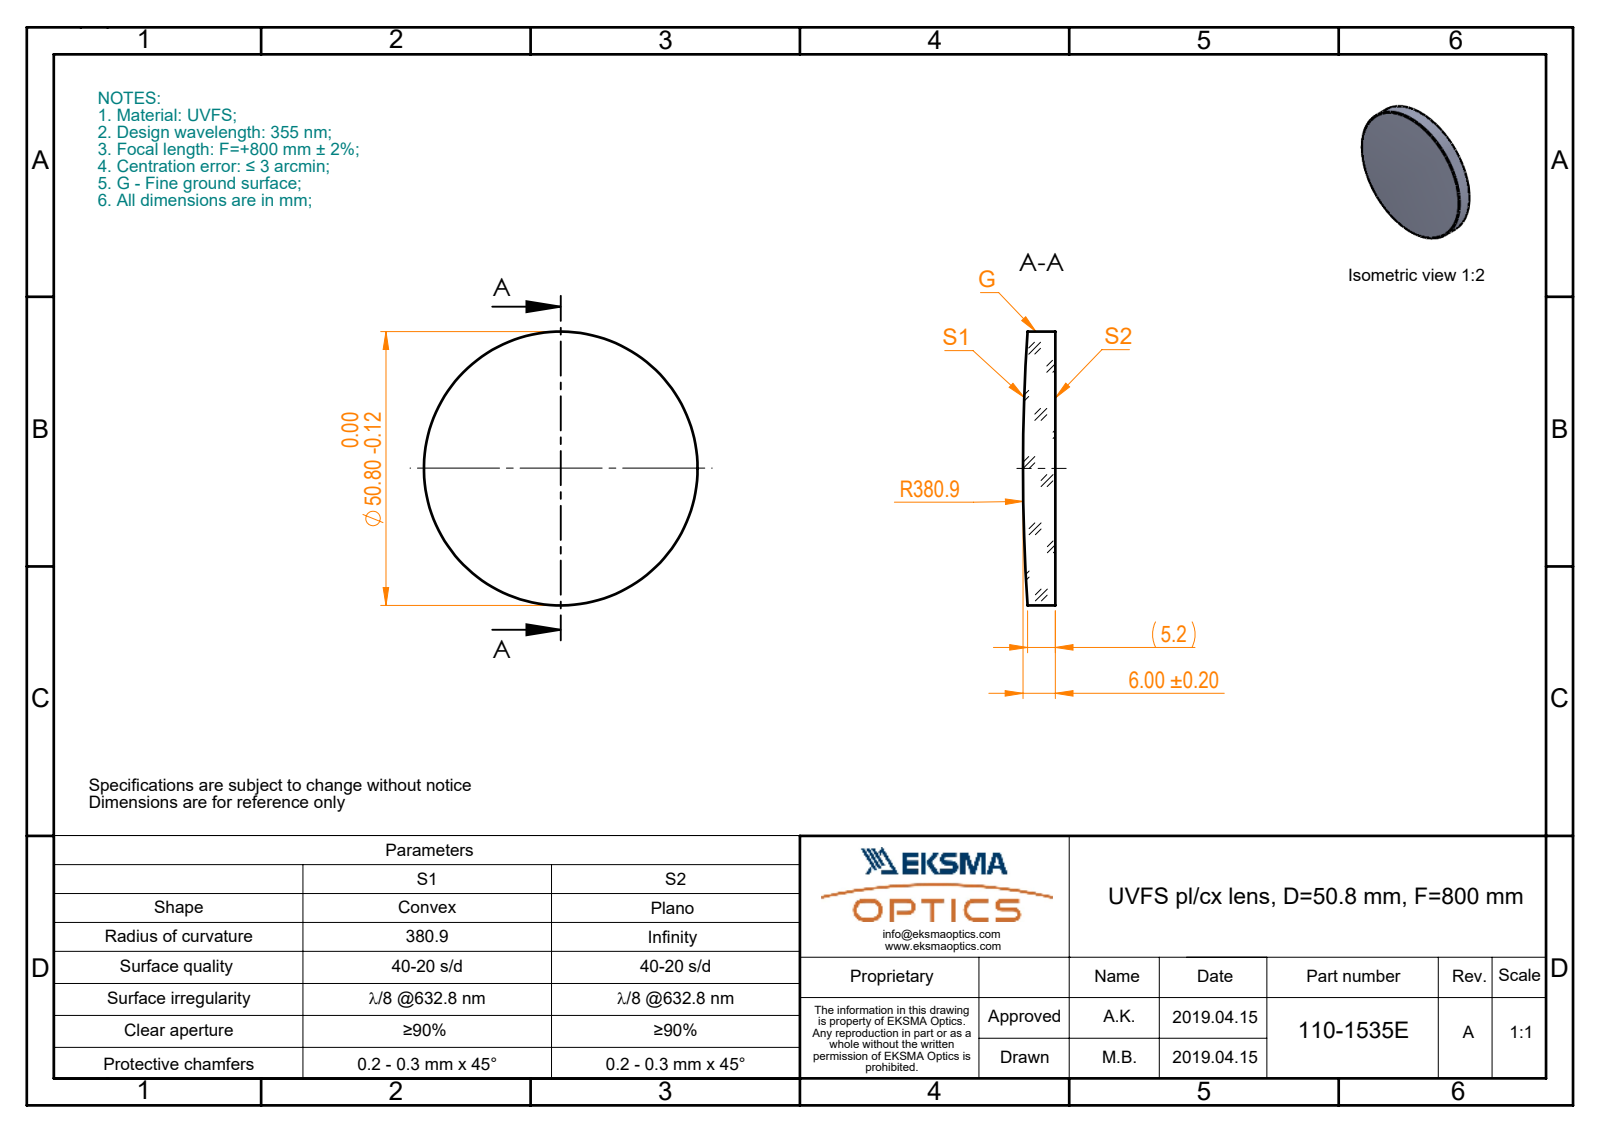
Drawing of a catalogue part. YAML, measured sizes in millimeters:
part_name: "110-1535E UVFS pl-cx 50.8 F800"
step_written_by: "SolidWorks 2017 (CONFIG_CONTROL_DESIGN)"
units: millimeters
bodies: {solids: 1, faces: 5, planar: 1, cylindrical: 2, other: 2}
overall_size: [50.8, 50.8, 6]
volume: 11302
surface_area: 4878
round_bosses_or_shafts:
  - {diameter: 50.8, count: 1}
